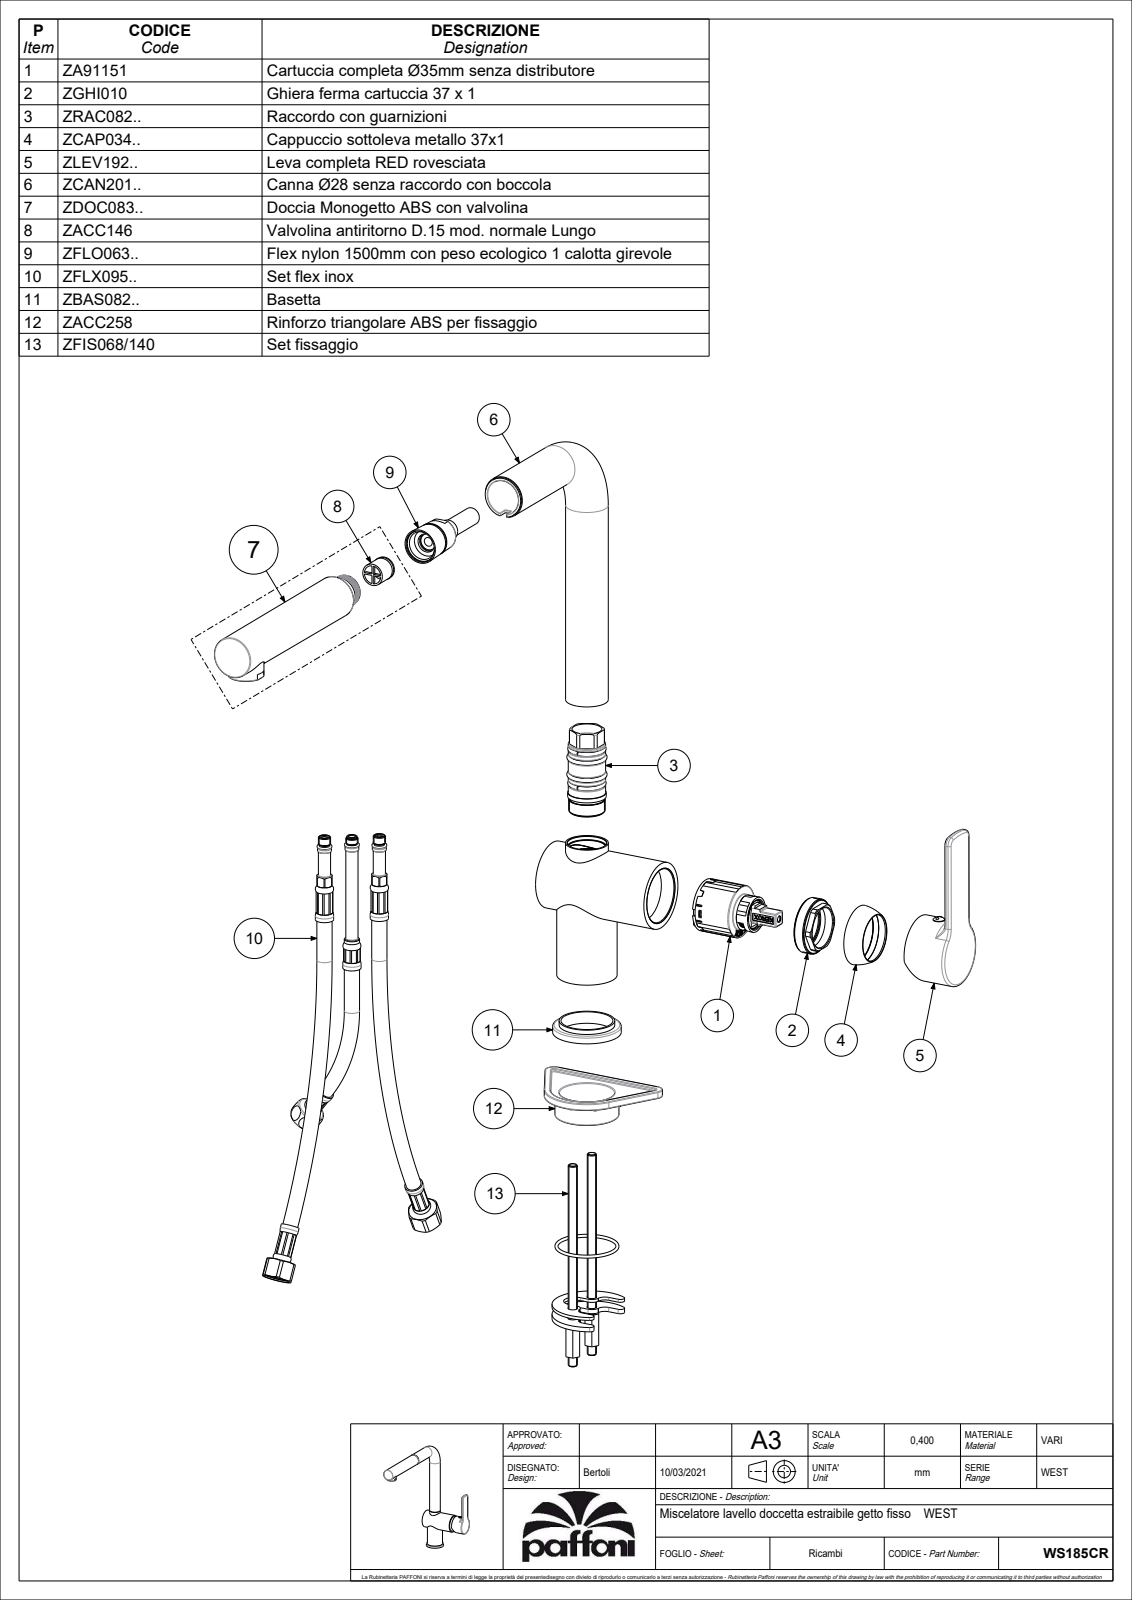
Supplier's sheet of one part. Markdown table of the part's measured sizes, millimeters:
| quantity | value |
| --- | --- |
| part name | WS185CR |
| STEP written by | CREO PARAMETRIC BY PTC INC, 2020044 (CONFIG_CONTROL_DESIGN) |
| units | millimeters |
| bodies | 2 solids, 4673 faces (2202 planar, 1813 cylindrical, 658 other) |
| overall size | 287 × 268.7 × 118.83 |
| volume | 228 204 mm³ |
| surface area | 180 692 mm² |
| round holes (diameter × count) | 0.4 × 480, 6.5 × 3, 7 × 3, 8.6 × 3, 9.4 × 3, 5.5 × 2, 8.5 × 2, 25 × 2, 25.7 × 2, 36 × 2, 3 × 1, 3.3 × 1 |
| round bosses / shafts (diameter × count) | 28 × 2, 23.5 × 2, 20 × 2, 18 × 2, 45 × 1, 44.7 × 1, 43 × 1, 39.6 × 1 |
| partial cylindrical surfaces (radius × count) | 0.5 × 95, 0.2 × 72, 0.3 × 27, 24.3 × 12, 1.5 × 9, 5 × 8, 1 × 7, 1.7 × 6 |
| main face-to-face distances | 4.5, 70.8, 4.46, 1.5, 15, 5.95, 11.2, 76.75, 55.8, 20.95 |
| hole center spacings | 8.16, 6.71, 1.34, 6.84, 7.41, 8.05, 10.48, 6.49 |
